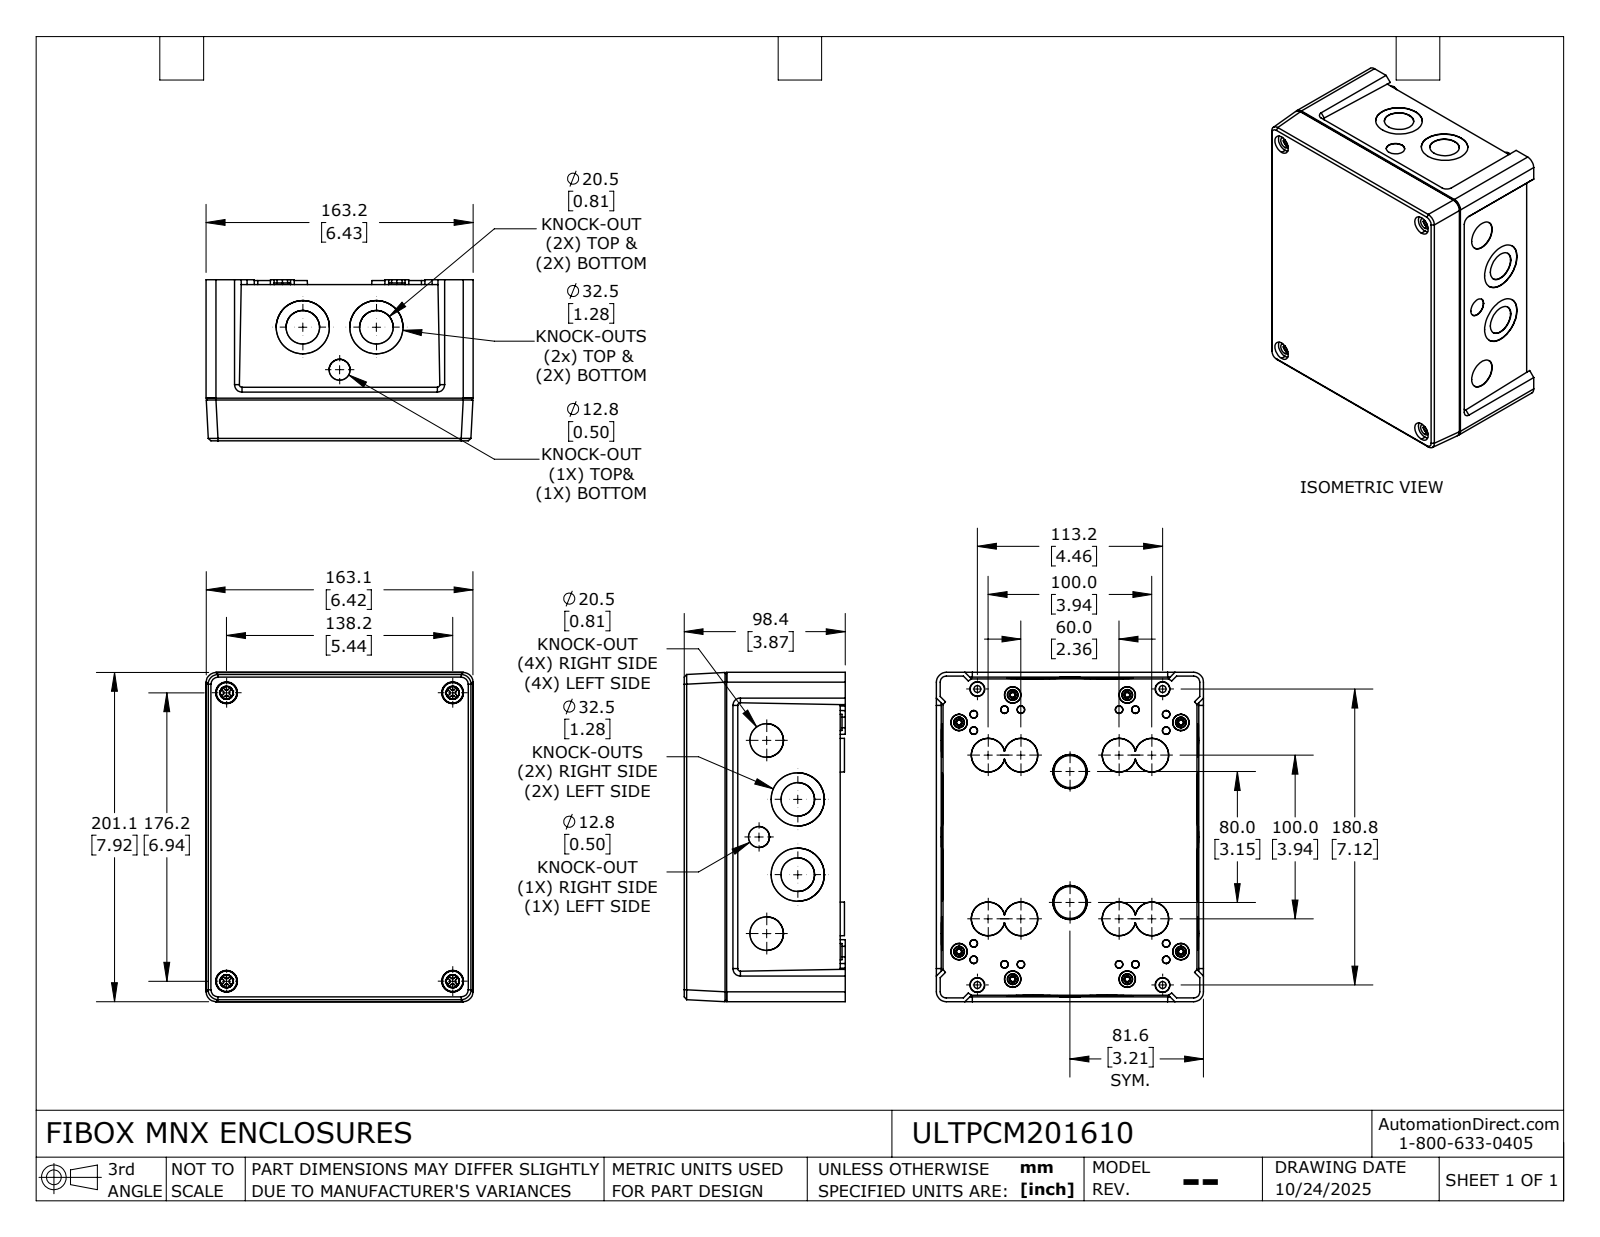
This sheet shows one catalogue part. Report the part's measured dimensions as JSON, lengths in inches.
{"part_name": "ULTPCM201610_Default", "step_written_by": "SolidWorks 2024 (CONFIG_CONTROL_DESIGN)", "units": "inches", "bodies": {"solids": 6, "faces": 1391, "planar": 557, "cylindrical": 204, "other": 630}, "overall_size": [7.921, 6.425, 3.874], "volume_in3": 31.63, "surface_area_in2": 461, "round_holes": [[0.807, 12], [1.28, 8], [0.352, 4], [0.504, 4]], "round_bosses_or_shafts": [[0.492, 8], [0.339, 4], [0.315, 4], [0.236, 4]], "partial_cylinders_radius": [[0.047, 16], [0.02, 10], [0.236, 8], [0.146, 4], [0.317, 4]], "face_to_face_distances": [0.11, 0.091, 0.094, 3.646, 3.756, 3.555, 3.665, 0.132, 2.732, 2.642], "hole_center_spacings": [1.3, 1.354, 1.602, 2.33, 3.314, 1.772, 1.811, 4.646]}
